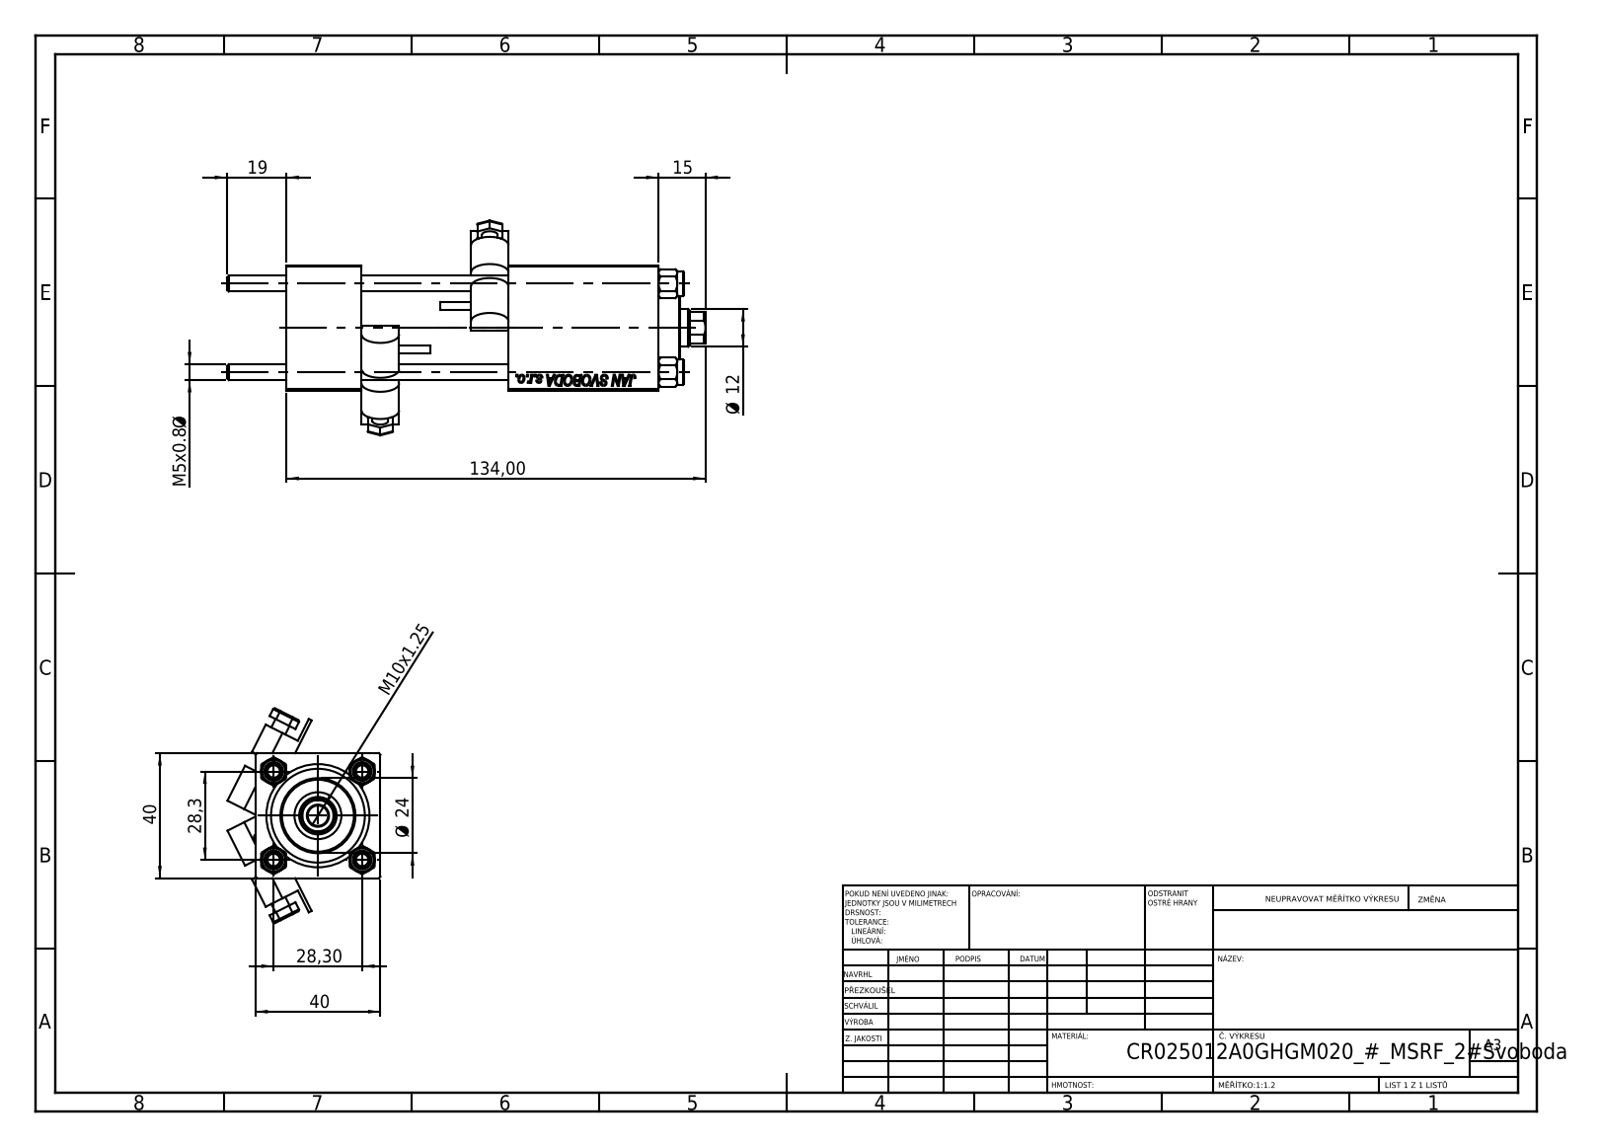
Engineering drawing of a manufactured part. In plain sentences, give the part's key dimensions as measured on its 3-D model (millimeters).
The part is named "MSRF_MSRG1; CR025_012_A_0_G_A_G_M_020_+#_##_TYCINKA; NUT_M5; V215_VC_A (+2 more)". Its 3-D file was written by "SolidWorks 2019 (CONFIG_CONTROL_DESIGN)". It is 13 solids with 1195 faces: 553 planar, 106 cylindrical and 536 other. Overall it measures 153 by 68.71 by 48.93 millimeters. Its volume is 151 725 cubic millimeters and its surface area 63 023 square millimeters. Round holes: 4 of diameter 5, 3 of diameter 20, 2 of diameter 7, 2 of diameter 13.16, 1 of diameter 6.5, 1 of diameter 12, 1 of diameter 15, 1 of diameter 25, 1 of diameter 30. Round bosses or shafts: 4 of diameter 8, 2 of diameter 5, 2 of diameter 2.5, 1 of diameter 31, 1 of diameter 24. Partial cylindrical surfaces (rounded edges, fillets, slot ends): 12 of radius 0.5, 4 of radius 6, 1 of radius 5.5. The main face-to-face distances are 40, 24, 71, 47, 95, 119, 48, 90.3, 66.3, 19.3. The hole center spacings are 20.01, 28.3, 40.02, 72.
